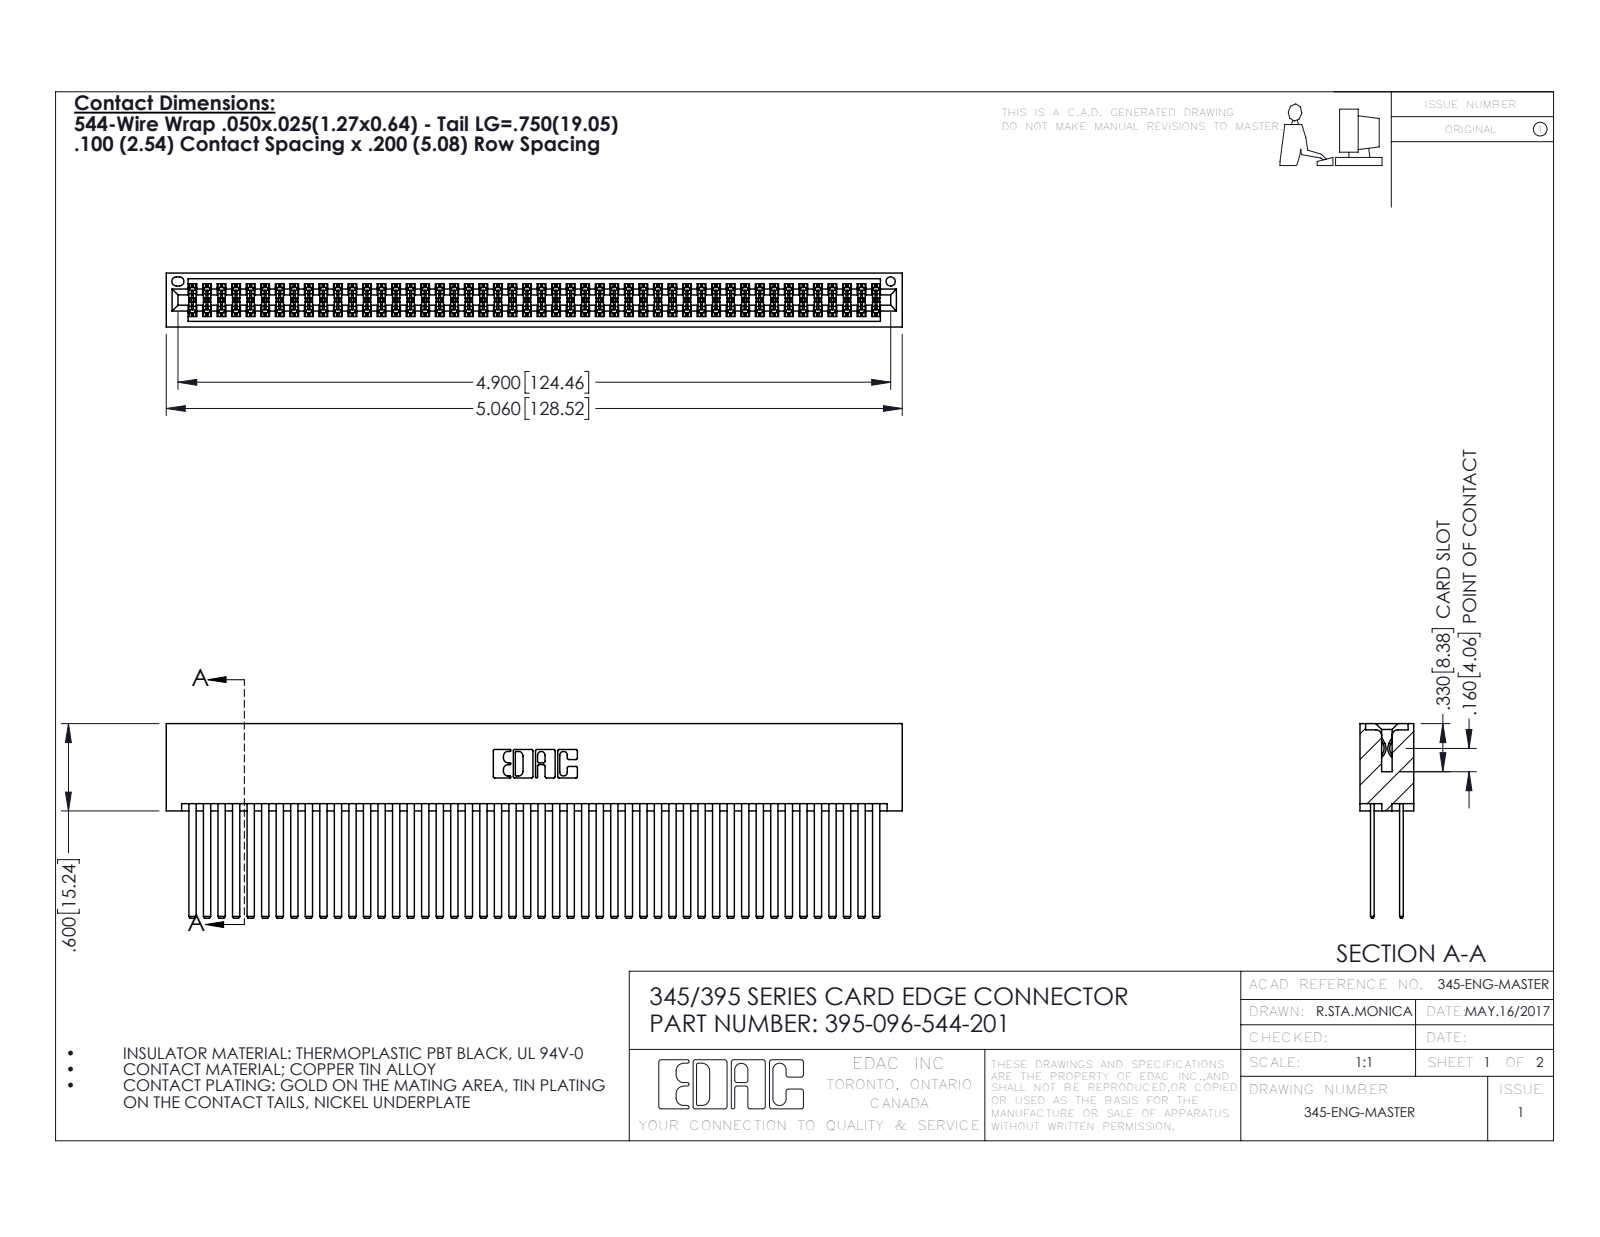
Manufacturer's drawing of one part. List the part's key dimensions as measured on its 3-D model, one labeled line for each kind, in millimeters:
Part name (STEP PRODUCT): 345 Part_No Mounting Lugs; 345-292-001_345-293-144; 395-096-544-201
STEP written by: SolidWorks 2016 (CONFIG_CONTROL_DESIGN)
Units: millimetres
Bodies: 97 solids, 4342 faces (2860 planar, 1482 cylindrical, 0 other)
Overall size (bounding box): 128.5 × 34 × 9.4
Volume: 14 500 mm³ · Surface area: 25 800 mm²
Round holes (diameter × count): ⌀1.6 ×1
Partial cylindrical surfaces — rounded edges, fillets, slot ends (radius × count): R0.2 ×144, R0.3 ×22, R0.2 ×6, R0.8 ×6, R0.7 ×3, R0.4 ×2, R0.5 ×2, R0.6 ×2
Main face-to-face distances: 5.1, 0.6, 7.6, 1.8, 2.5, 6.9, 5.7, 4.4, 9.4, 1.3
